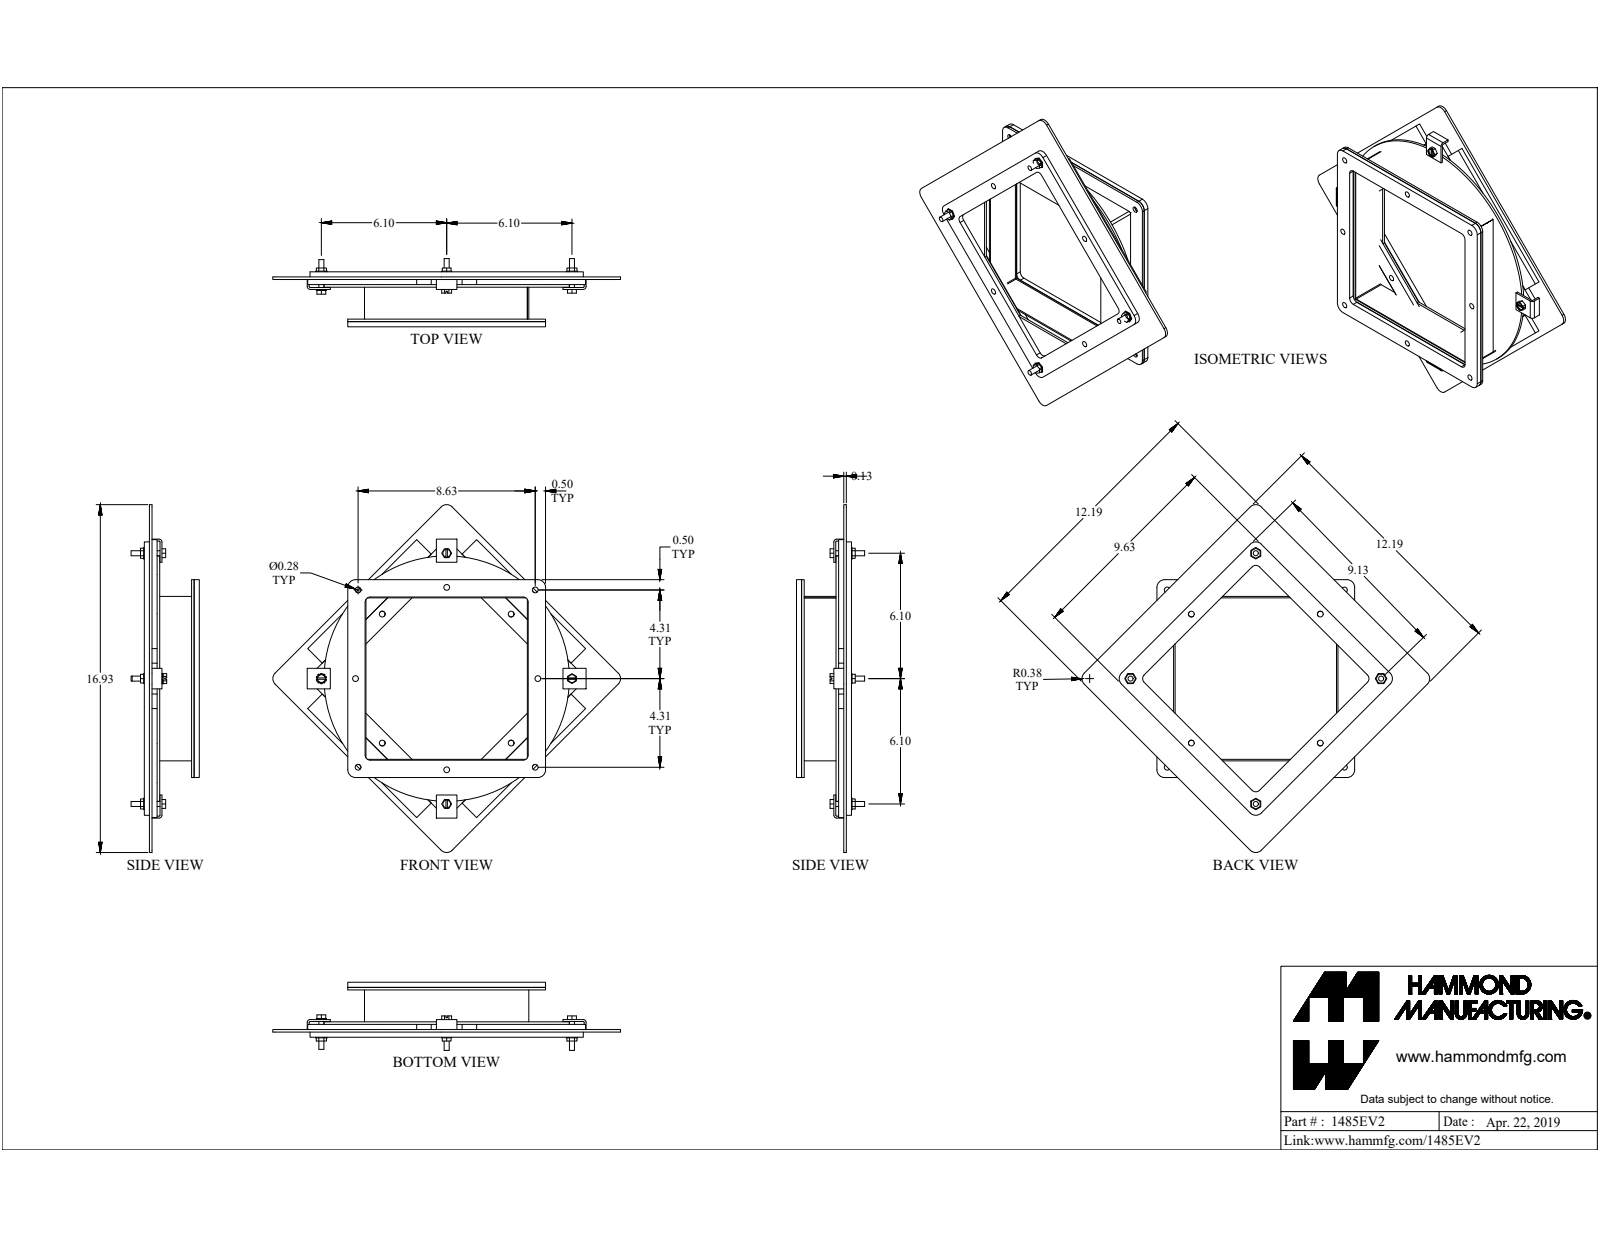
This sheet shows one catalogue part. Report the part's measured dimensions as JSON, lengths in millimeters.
{"part_name": "1485EV2", "step_written_by": "SolidWorks 2019 (CONFIG_CONTROL_DESIGN)", "units": "millimeters", "bodies": {"solids": 33, "faces": 532, "planar": 366, "cylindrical": 150, "other": 16}, "overall_size": [429.9, 429.9, 84.3], "volume_mm3": 954900, "surface_area_mm2": 562500, "round_holes": [[7.1, 16], [9.5, 6], [5, 5], [7.9, 4], [4.7, 2], [6.7, 2], [8, 2], [5.7, 1], [6.6, 1]], "round_bosses_or_shafts": [[6.2, 5], [14.3, 2], [6.4, 2], [303.2, 1]], "partial_cylinders_radius": [[9.5, 12], [1.2, 9], [3.6, 9], [6.4, 9], [1.6, 4], [0.9, 3], [2.7, 3], [1.5, 1]], "face_to_face_distances": [6.4, 9.5, 3.2, 52.1, 3.2, 42.6, 9.5, 48.9, 61.6, 45.7], "hole_center_spacings": [247.8, 42.2, 86.3, 109.6, 109.6, 118.6, 159.4, 191.6]}
